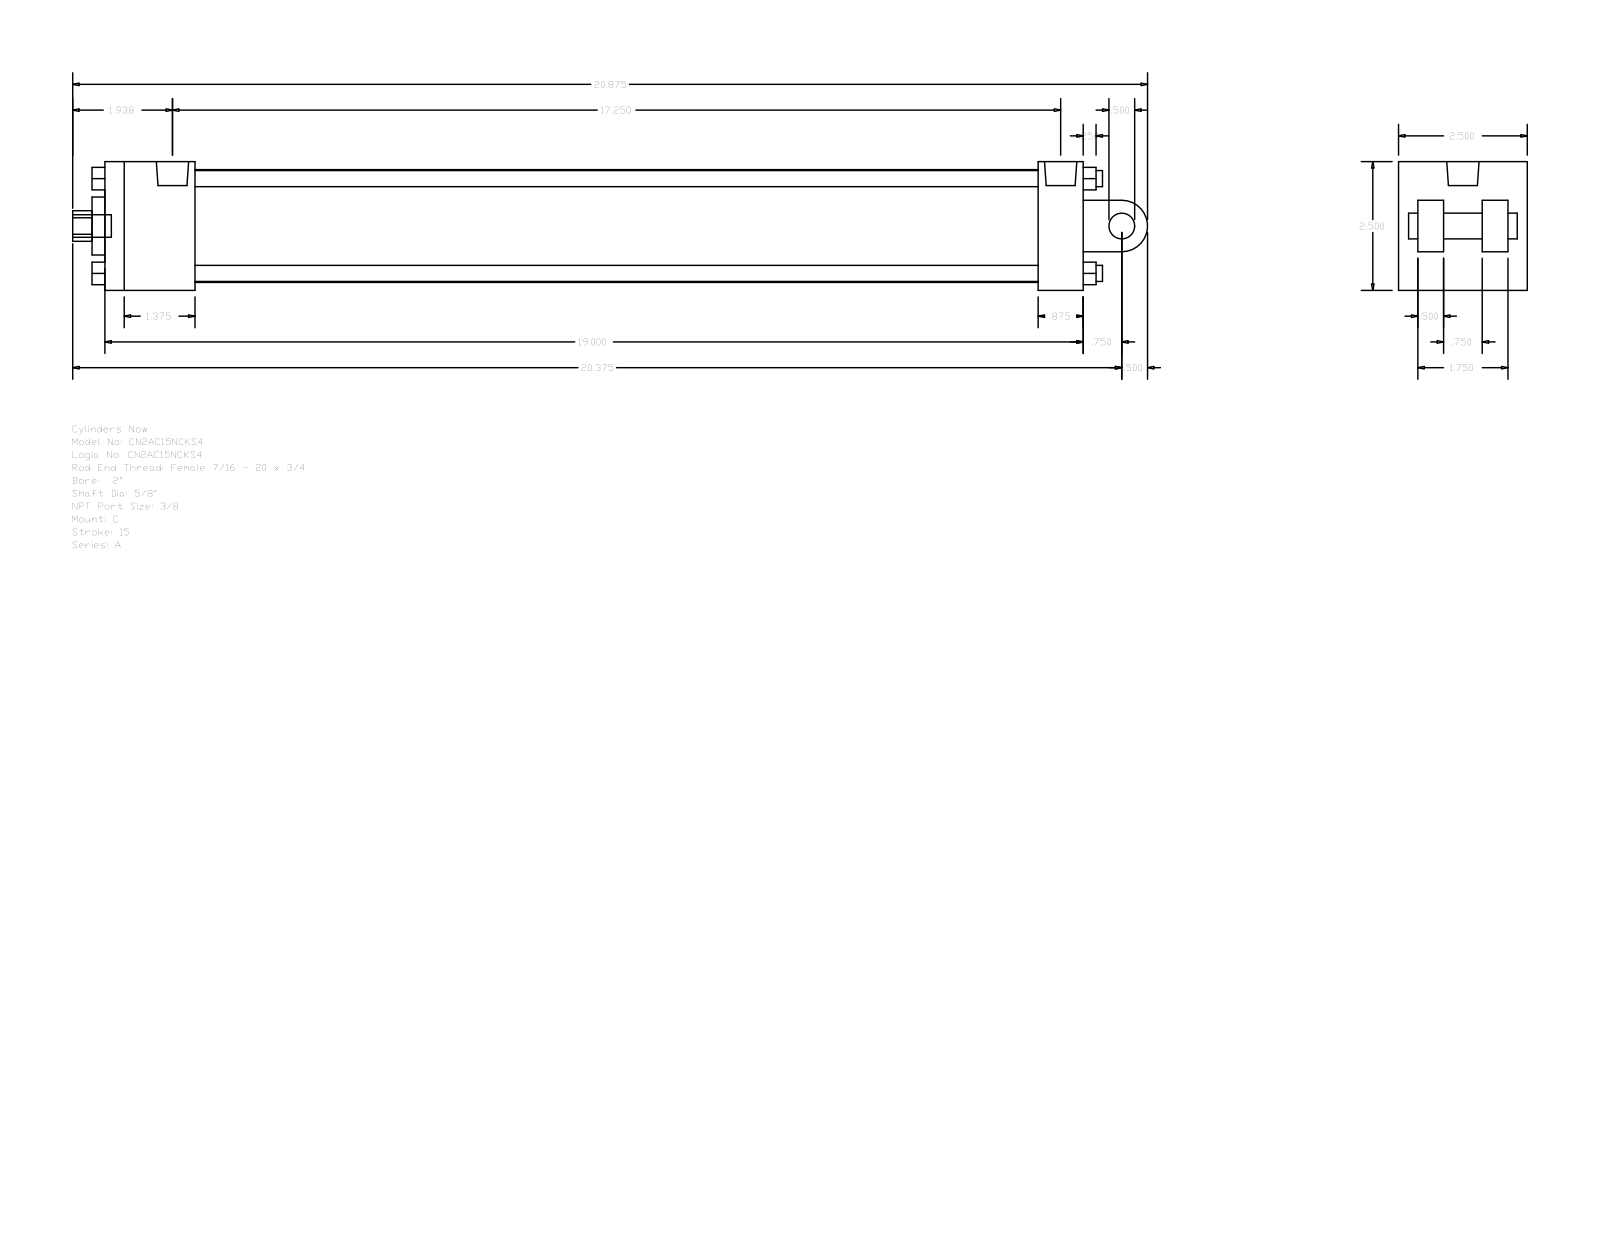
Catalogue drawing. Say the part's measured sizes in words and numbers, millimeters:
The part is named "A_C__0200_0.625". Its 3-D file was written by "GSSL Pune (CONFIG_CONTROL_DESIGN)". It is 0 solids with 135 faces: 102 planar, 33 cylindrical and 0 other. Overall it measures 530.23 by 63.5 by 63.5 millimeters. Round holes: 2 of diameter 5.56, 1 of diameter 15.88, 1 of diameter 15.93, 1 of diameter 28.57, 1 of diameter 55.63. Round bosses or shafts: 4 of diameter 7.94, 2 of diameter 5.56, 1 of diameter 15.93, 1 of diameter 12.7, 1 of diameter 11.11. Partial cylindrical surfaces (rounded edges, fillets, slot ends): 1 of radius 7.54, 1 of radius 12.7. The main face-to-face distances are 63.5, 482.6, 44.45, 9.52, 438.15, 460.37, 415.92, 22.23, 12.7, 41.28. The hole center spacings are 3.97.
